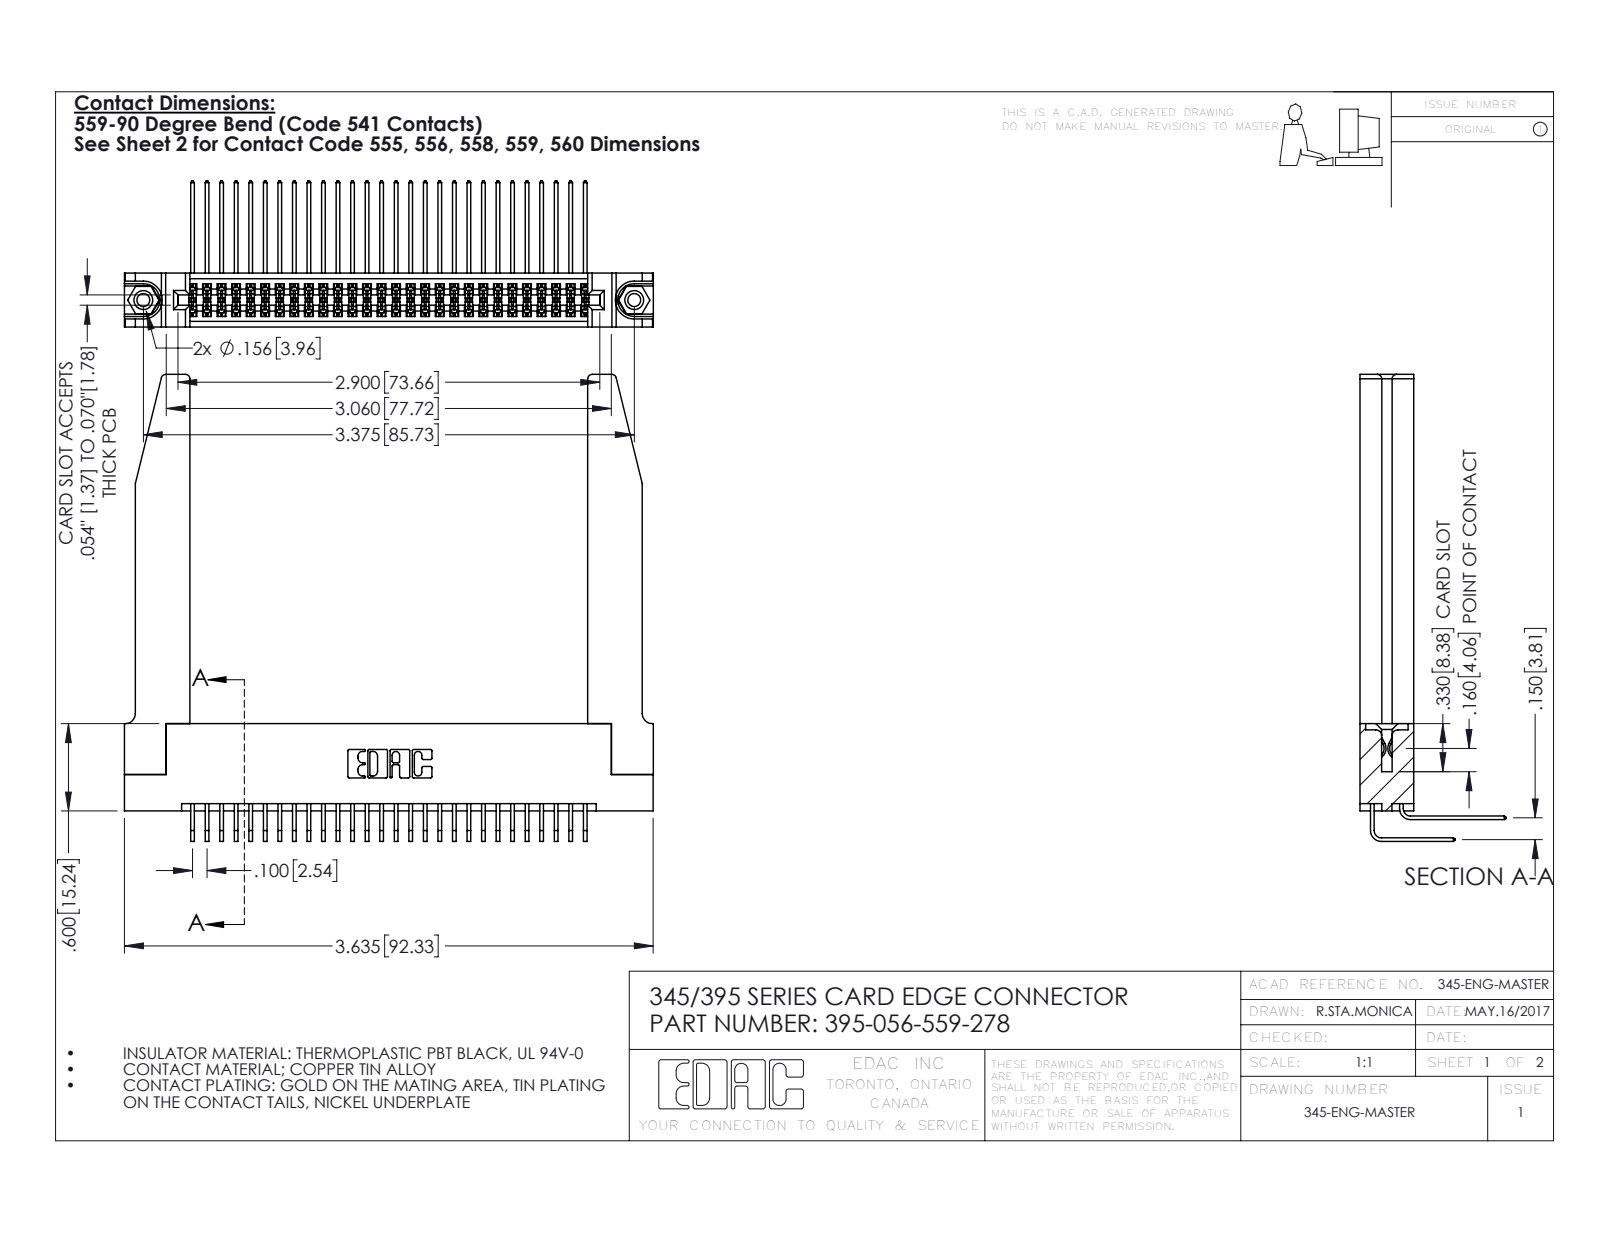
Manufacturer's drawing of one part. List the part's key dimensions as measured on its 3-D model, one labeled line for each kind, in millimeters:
Part name (STEP PRODUCT): 345-220-078_345-220-078; 345-292-001_559 Tail - 2; 345-292-001_558 559 Tail - 1; 395-056-559-278 (+2 more)
STEP written by: SolidWorks 2016 (CONFIG_CONTROL_DESIGN)
Units: millimetres
Bodies: 61 solids, 3272 faces (2182 planar, 1038 cylindrical, 52 other)
Overall size (bounding box): 92.4 × 81.5 × 25.5
Volume: 16 930 mm³ · Surface area: 21 630 mm²
Round holes (diameter × count): ⌀2.3 ×2, ⌀3.2 ×2, ⌀4 ×2, ⌀1.6 ×1
Round bosses / shafts (diameter × count): ⌀3.9 ×2
Partial cylindrical surfaces — rounded edges, fillets, slot ends (radius × count): R0.2 ×111, R0.3 ×22, R0.8 ×8, R0.2 ×6, R0.8 ×6, R0.7 ×3, R0.4 ×2, R0.5 ×2
Main face-to-face distances: 9.4, 1.8, 7.6, 5.1, 2.5, 6.9, 0.6, 5.7, 3.8, 4.4
Hole centre spacings: 6.9, 79.8, 85.7
